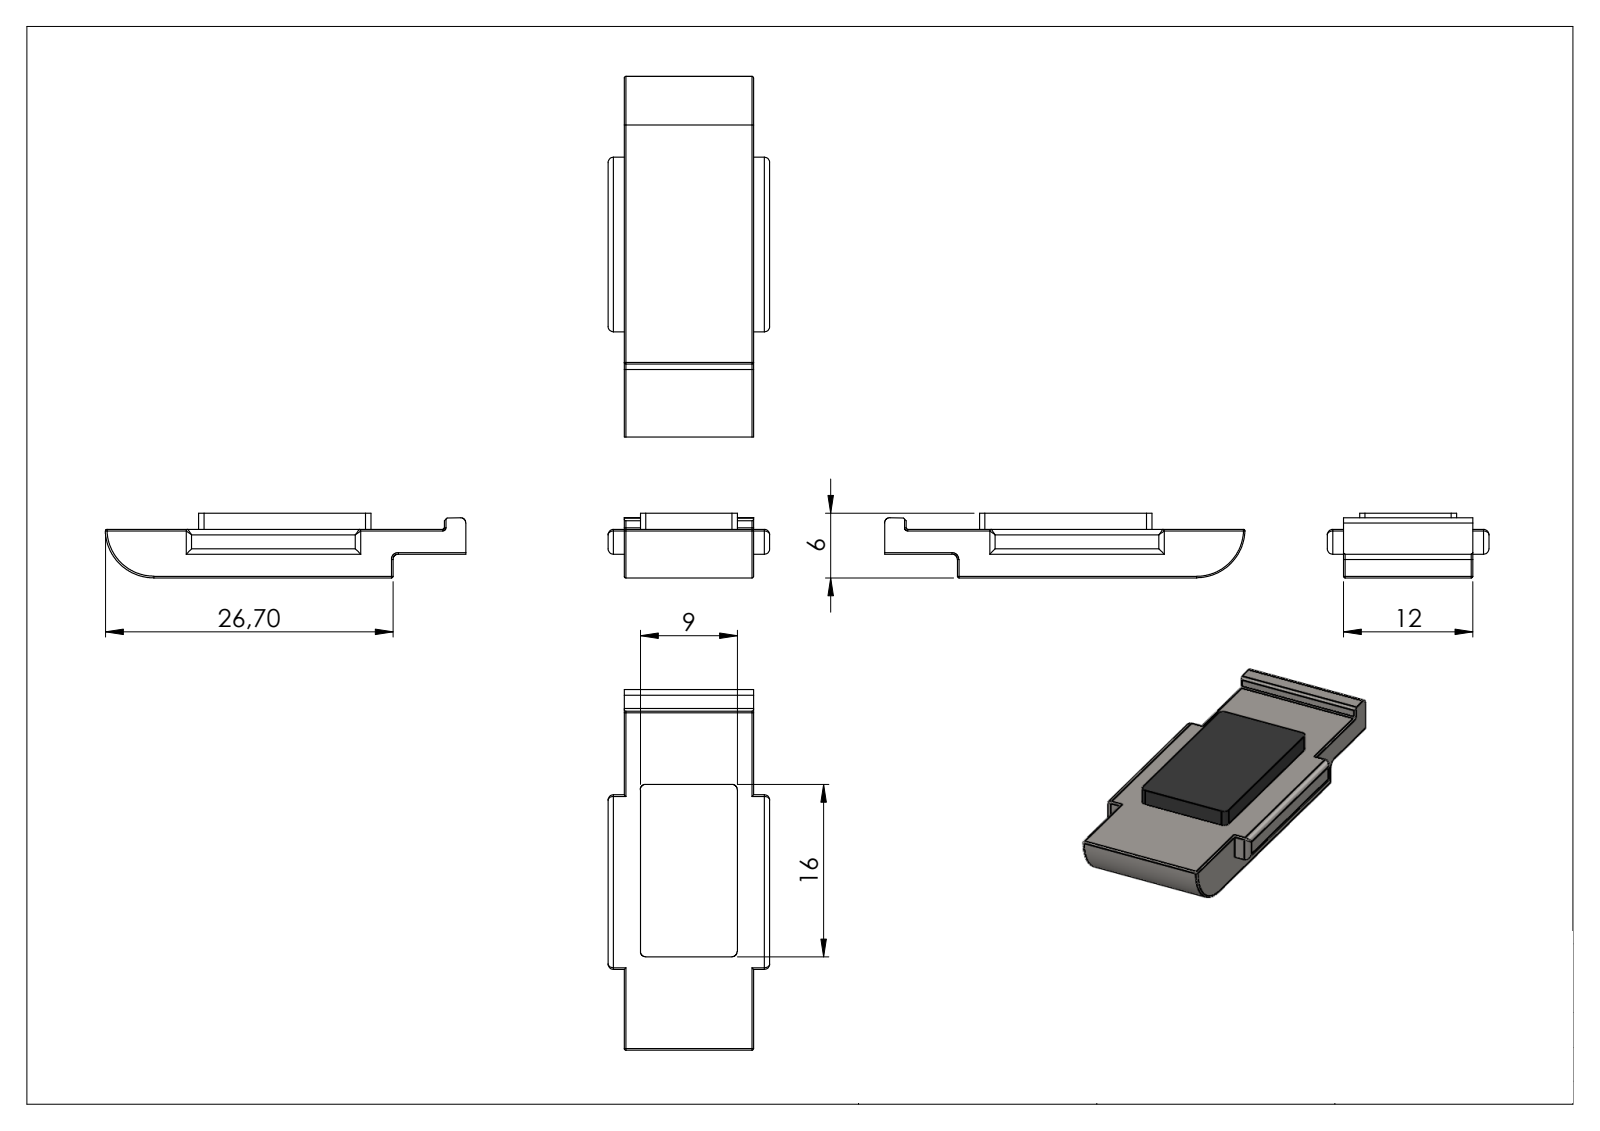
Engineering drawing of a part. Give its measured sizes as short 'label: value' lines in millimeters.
name: 31-BODEN-ZN0
written by: SolidWorks 2018 (CONFIG_CONTROL_DESIGN)
unit: mm
bodies: 1 solid, 71 faces (23 planar, 34 cylindrical, 14 other)
size: 33.46 × 15 × 6
volume: 1 925 mm³; area: 1 332 mm²
rounds: 15× R0.15, 14× R0.5, 1× R4.5
face distances: 4.5, 1.5, 6, 12, 2.2, 2.3, 3.8, 10.5, 3, 13.5
